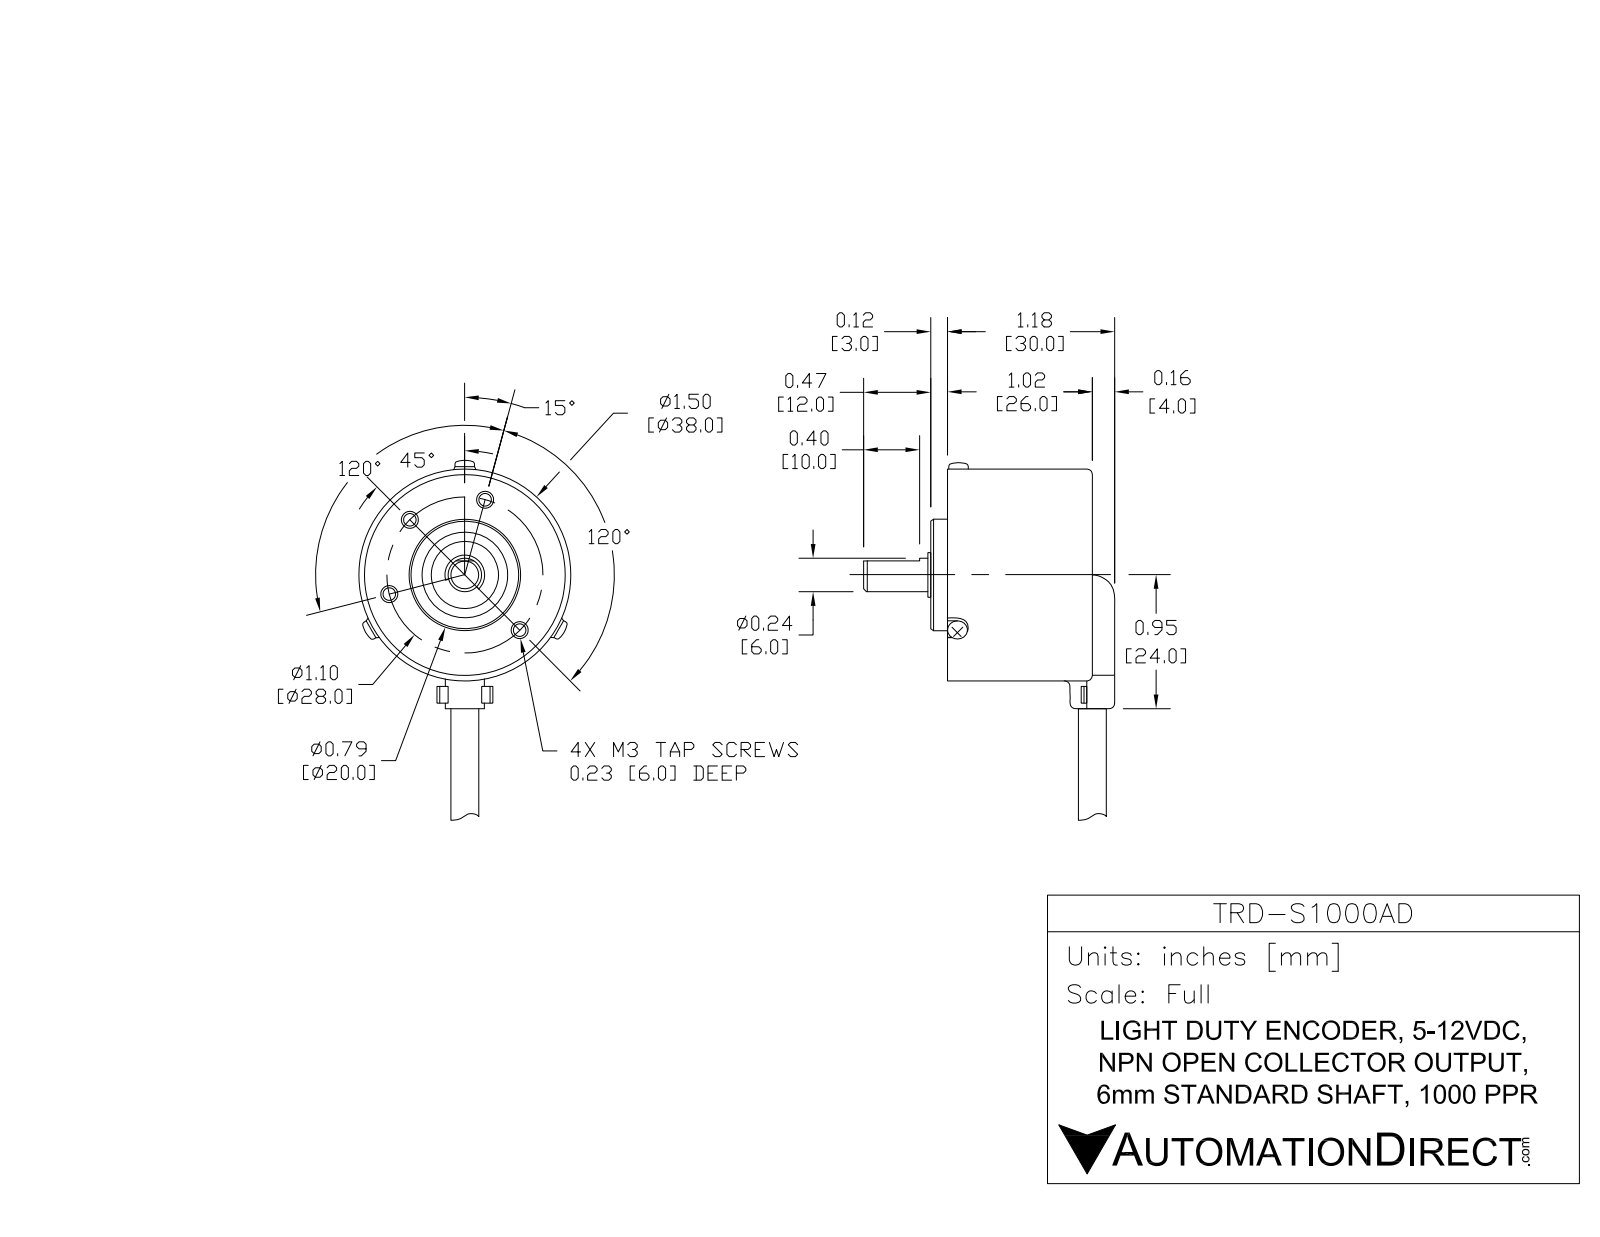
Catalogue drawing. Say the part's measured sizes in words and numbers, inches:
The part is named "TRD-S1000AD". Its 3-D file was written by "SolidWorks 2016 (AUTOMOTIVE_DESIGN)". It is 3 solids with 257 faces: 98 planar, 100 cylindrical and 59 other. Overall it measures 7.189 by 1.768 by 1.496 inches. Its volume is 2.068 cubic inches and its surface area 13.85 square inches. Round holes: 4 of diameter 0.118, 1 of diameter 0.205, 1 of diameter 0.256, 1 of diameter 1.409. Round bosses or shafts: 1 of diameter 1.496, 1 of diameter 0.787, 1 of diameter 0.591, 1 of diameter 0.315, 1 of diameter 0.236, 1 of diameter 0.197, 1 of diameter 0.193. Partial cylindrical surfaces (rounded edges, fillets, slot ends): 11 of radius 0.016, 4 of radius 0.004, 3 of radius 0.13, 3 of radius 0.748, 2 of radius 0.008, 2 of radius 0.02, 2 of radius 0.146, 1 of radius 0.11. The main face-to-face distances are 1.024, 0.118, 1.142, 0.02, 0.138, 0.803, 1.161, 0.354, 0.335, 0.217. The hole center spacings are 0.551, 0.955, 0.954, 1.102.
